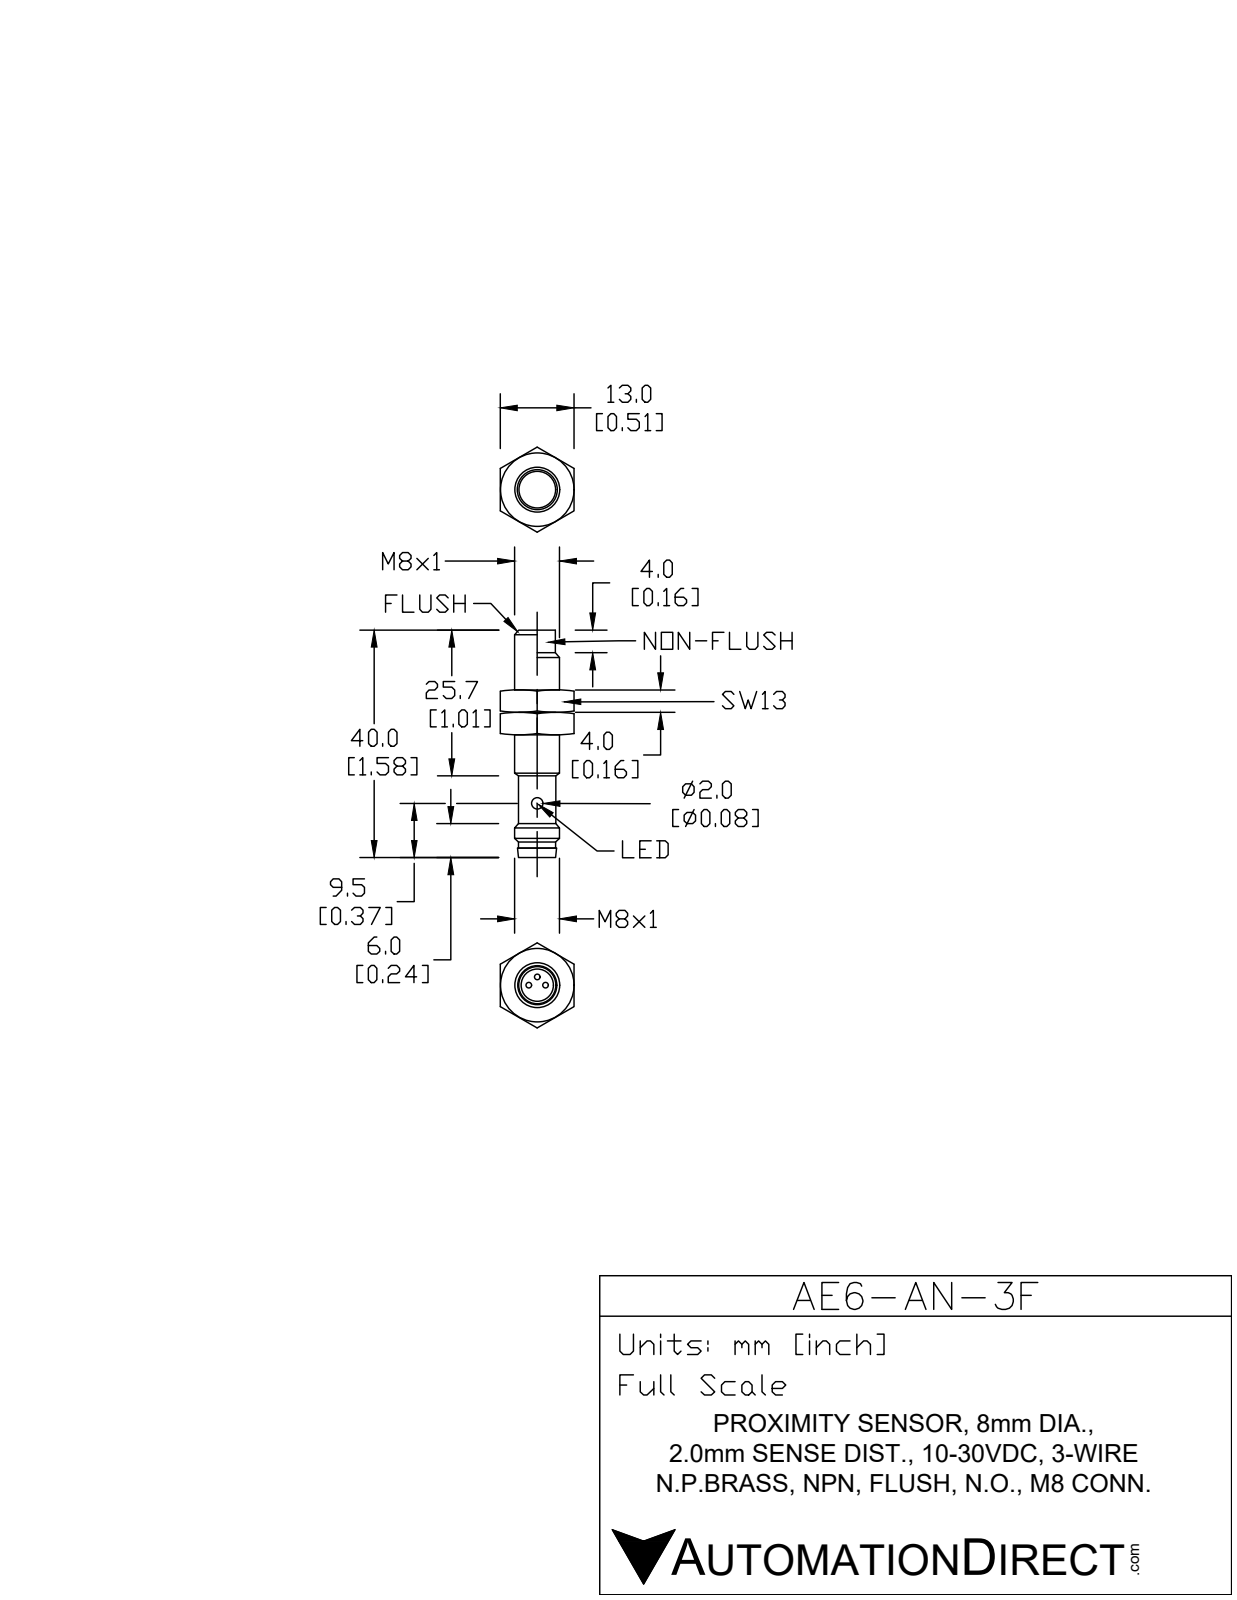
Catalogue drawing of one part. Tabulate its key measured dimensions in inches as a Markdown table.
| quantity | value |
| --- | --- |
| part name | AE6-AN-3F |
| STEP written by | SolidWorks 2017 (AUTOMOTIVE_DESIGN) |
| units | inches |
| bodies | 3 solids, 61 faces (11 planar, 30 cylindrical, 20 other) |
| overall size | 1.575 × 0.315 × 0.315 |
| volume | 0.109 in³ |
| surface area | 2.26 in² |
| round holes (diameter × count) | 0.079 × 4, 0.228 × 1 |
| round bosses / shafts (diameter × count) | 0.039 × 3, 0.315 × 1, 0.272 × 1, 0.256 × 1, 0.23 × 1 |
| main face-to-face distances | 1.122, 1.11, 1.299, 1.287, 0.177, 1.378, 1.366, 0.256, 0.079, 1.575 |
